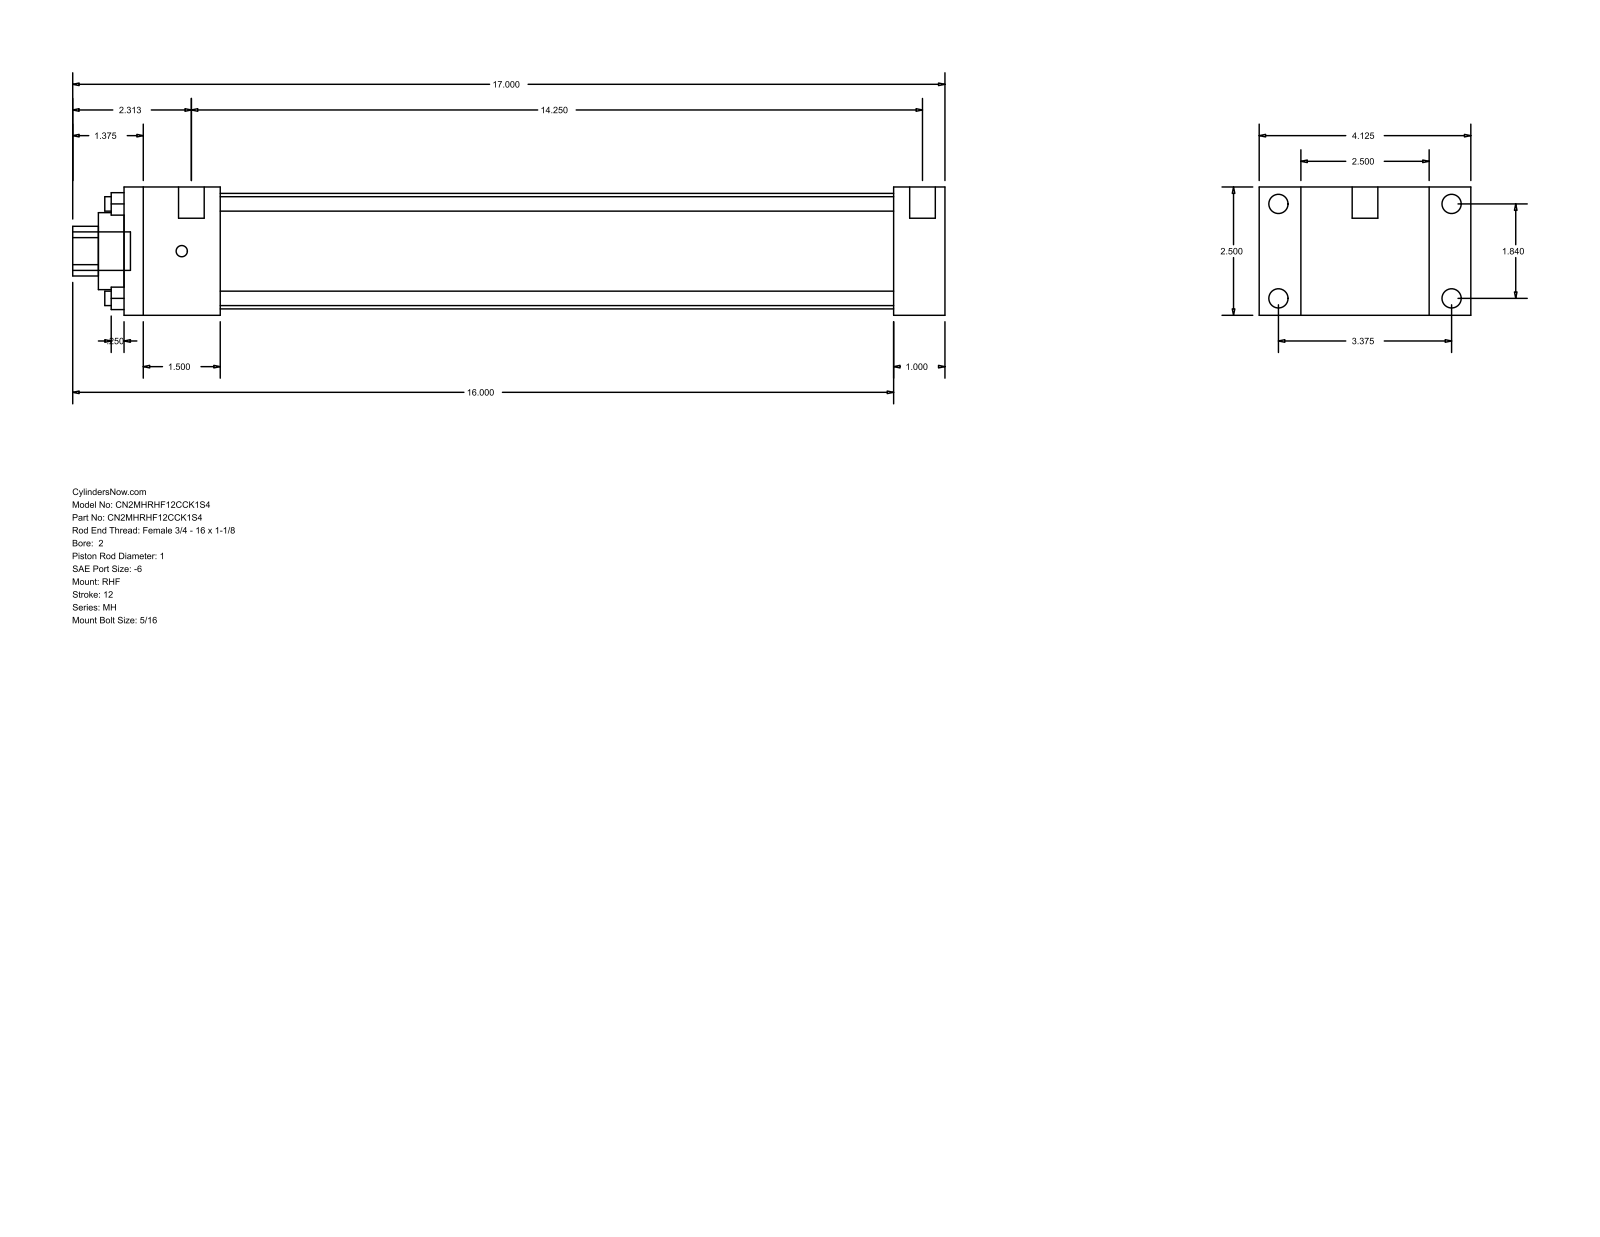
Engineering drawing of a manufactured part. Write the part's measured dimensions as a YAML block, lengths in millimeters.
part_name: "MH_RHF__0200_1"
step_written_by: "GSSL Pune (CONFIG_CONTROL_DESIGN)"
units: millimeters
bodies: {solids: 0, faces: 88, planar: 60, cylindrical: 28, other: 0}
overall_size: [431.8, 104.78, 63.5]
round_holes:
  - {diameter: 7.14, count: 4}
  - {diameter: 25.4, count: 1}
  - {diameter: 38.1, count: 1}
  - {diameter: 57.15, count: 1}
round_bosses_or_shafts:
  - {diameter: 9.53, count: 4}
  - {diameter: 5.56, count: 4}
  - {diameter: 12.7, count: 2}
  - {diameter: 19.05, count: 1}
partial_cylinders:
  - {radius: 12.29, count: 1}
face_to_face_distances: [63.5, 25.4, 20.64, 84.14, 406.4, 381, 104.78, 47.63, 333.37, 358.77]
hole_center_spacings: [33.05, 46.74, 66.1]
